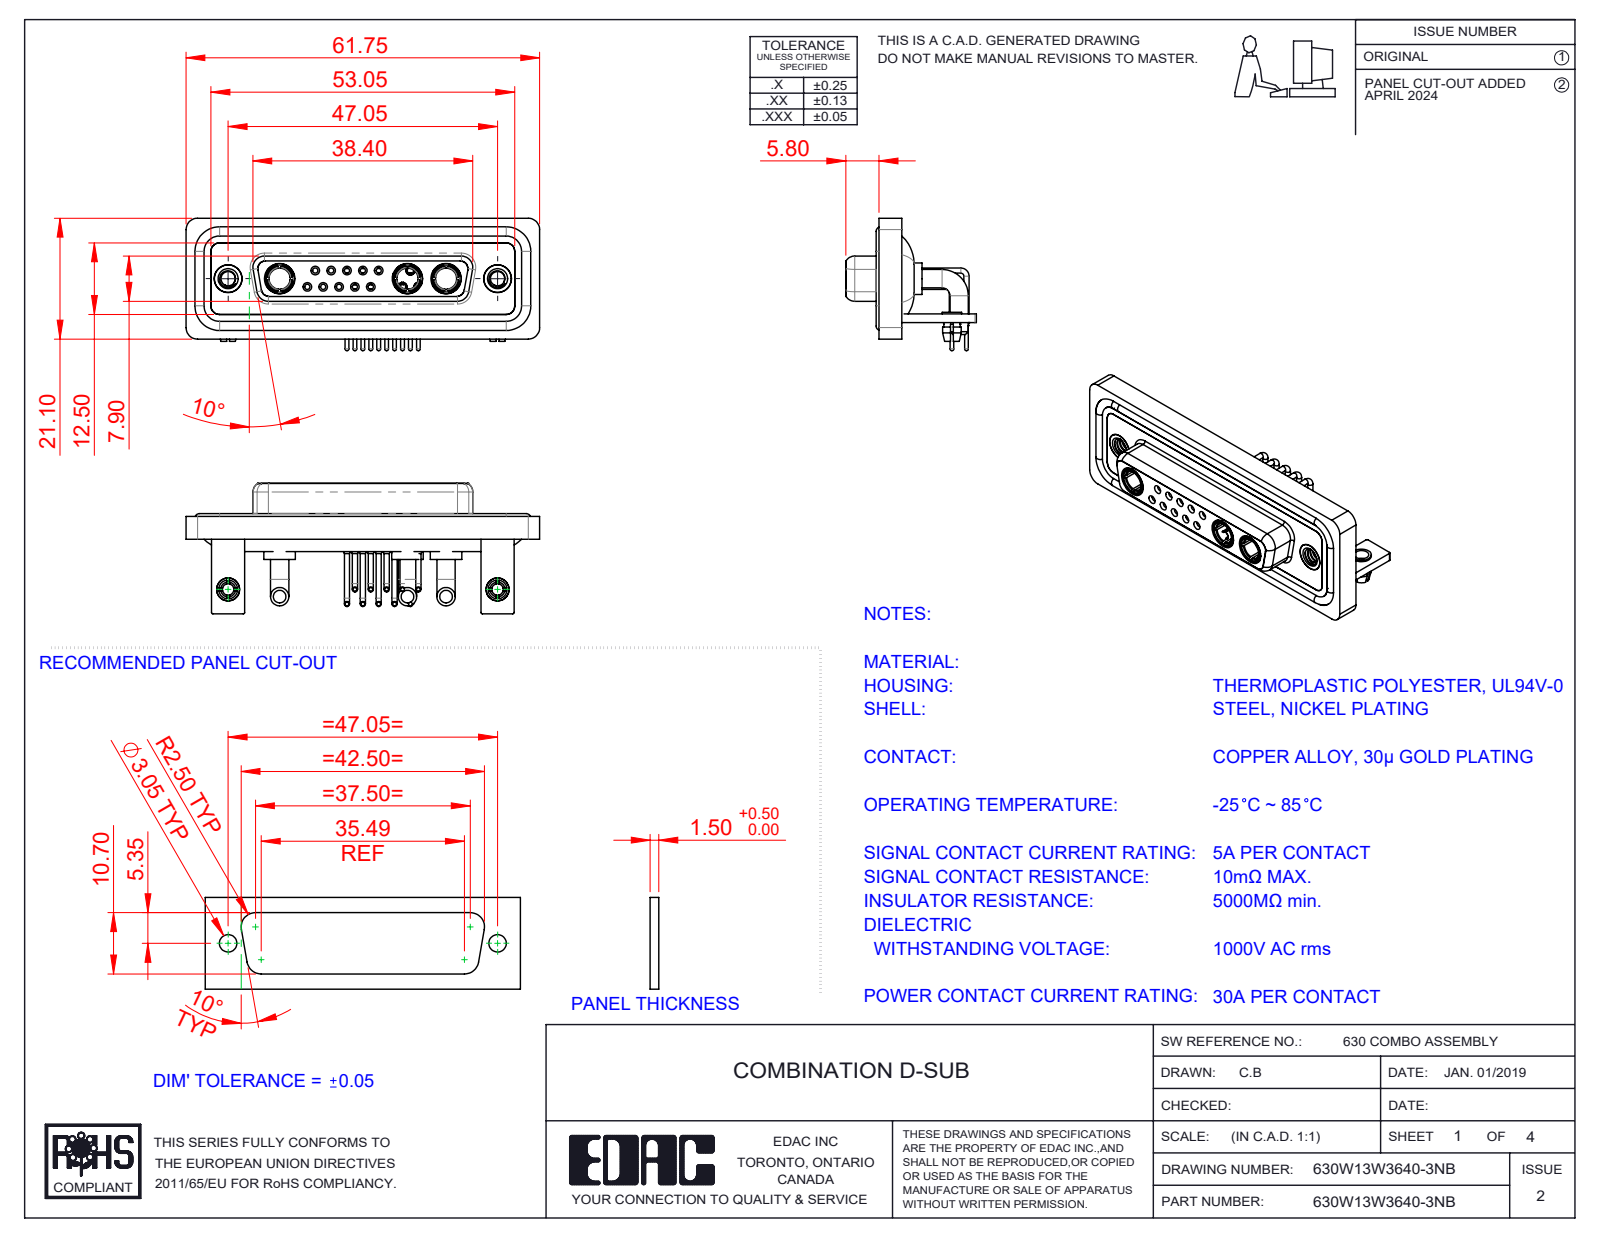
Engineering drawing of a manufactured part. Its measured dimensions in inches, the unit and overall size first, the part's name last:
Units: inches
Overall size (bounding box): 2.431 × 0.91 × 0.898
Round holes (diameter × count): ⌀0.079 ×12, ⌀0.035 ×10, ⌀0.043 ×10, ⌀0.059 ×10, ⌀0.063 ×5, ⌀0.067 ×5, ⌀0.191 ×5, ⌀0.098 ×4, ⌀0.146 ×3, ⌀0.209 ×3, ⌀0.126 ×2, ⌀0.157 ×2
Round bosses / shafts (diameter × count): ⌀0.035 ×15, ⌀0.063 ×12, ⌀0.026 ×10, ⌀0.126 ×6, ⌀0.079 ×5, ⌀0.059 ×5, ⌀0.217 ×3, ⌀0.205 ×3
Partial cylindrical surfaces — rounded edges, fillets, slot ends (radius × count): R0.079 ×19, R0.059 ×18, R0.01 ×16, R0.053 ×8, R0.063 ×8, R0.02 ×5, R0.024 ×4, R0.026 ×4
Main face-to-face distances: 0.016, 0.071, 0.114, 0.146, 0.059, 0.161, 0.043, 0.055, 0.063, 0.122
Hole centre spacings: 0.124, 0.109, 0.218, 0.198, 0.327, 0.198, 0.295, 0.436
Volume: 0.546 in³ · Surface area: 23.72 in²
Bodies: 27 solids, 1284 faces (410 planar, 547 cylindrical, 327 other)
Part name (STEP PRODUCT): 630Combo Housing_13W3; 630Combo Shell Rear_25 Contacts; 630Combo Stabilizer Bracket_50 Contacts; 630Combo Shell Front_25 Contacts (+7 more)
STEP written by: SolidWorks 2023 (CONFIG_CONTROL_DESIGN)
